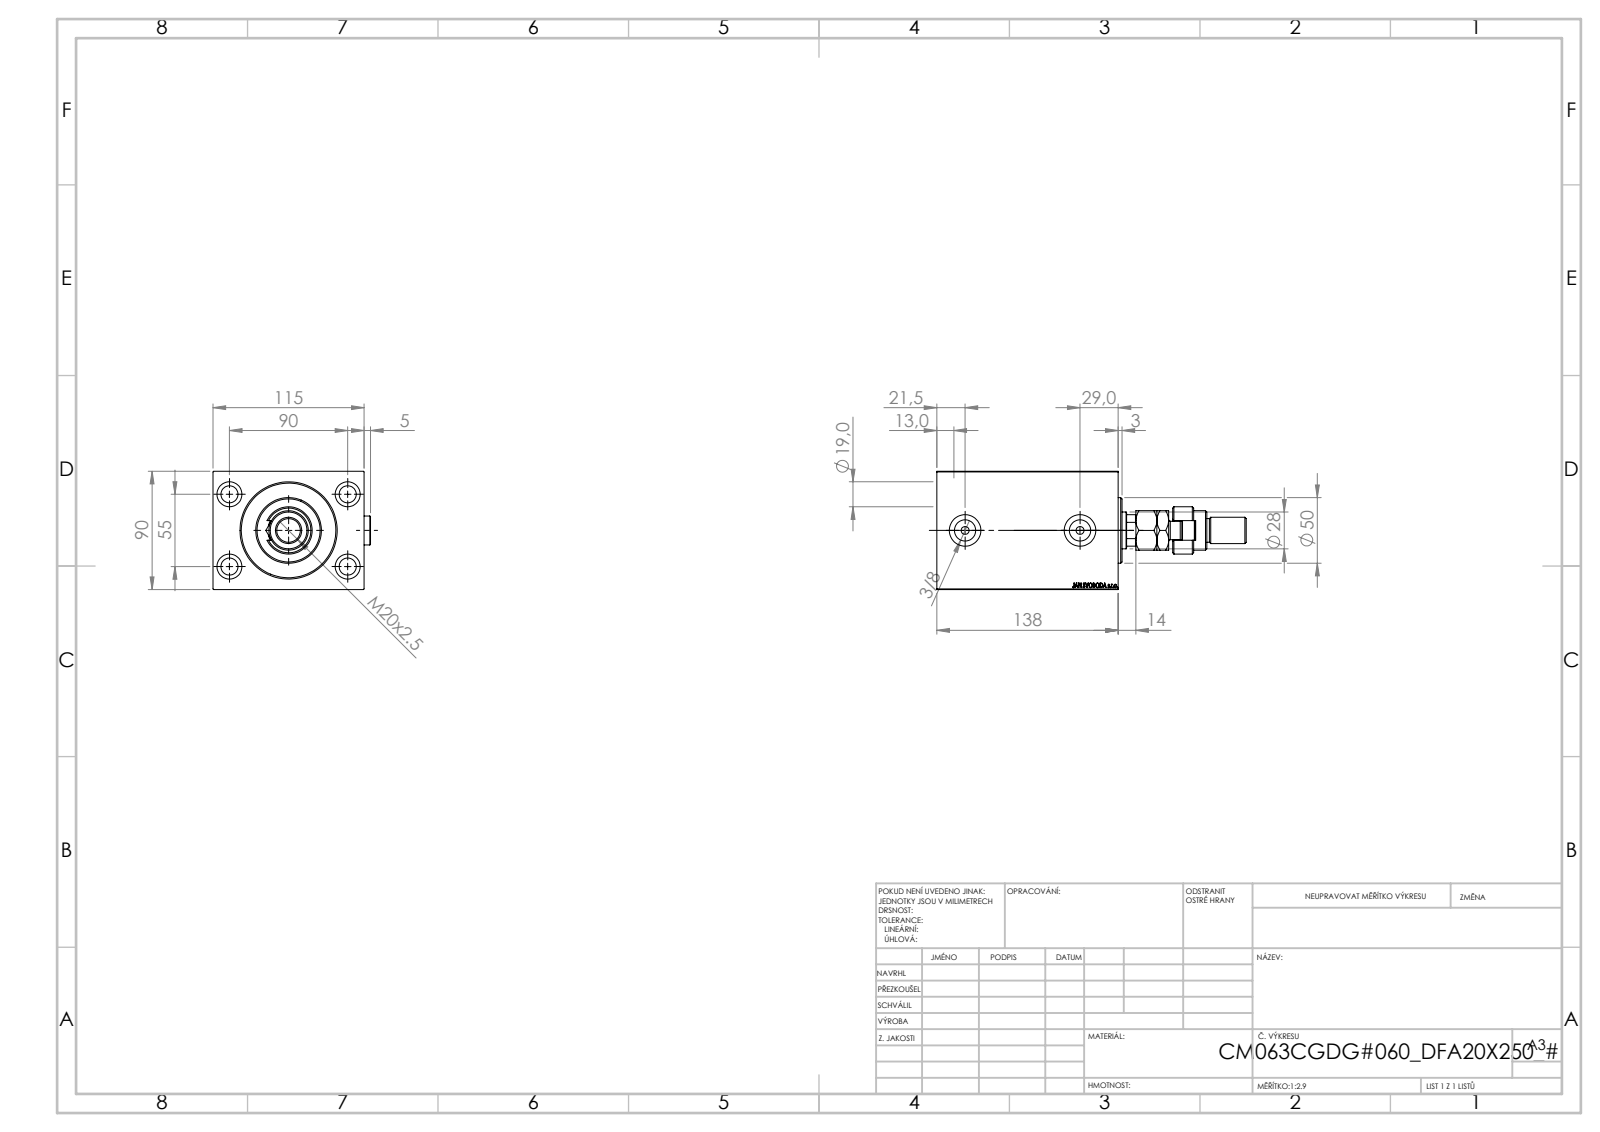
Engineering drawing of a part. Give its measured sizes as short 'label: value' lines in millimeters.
name: Zatka_OIL_PORT; MFA; V450CM_C_VCP; V450CM_VC_B (+2 more)
written by: SolidWorks 2019 (CONFIG_CONTROL_DESIGN)
unit: mm
bodies: 7 solids, 1004 faces (471 planar, 91 cylindrical, 442 other)
size: 235.5 × 119.9 × 90
volume: 1 233 000 mm³; area: 179 836 mm²
holes: 4× ⌀13, 4× ⌀19, 2× ⌀6, 2× ⌀16.17, 2× ⌀24, 1× ⌀18.5, 1× ⌀28, 1× ⌀31.5, 1× ⌀63, 1× ⌀65, 1× ⌀72
bosses: 3× ⌀22, 1× ⌀50, 1× ⌀36, 1× ⌀30, 1× ⌀20, 1× ⌀18, 1× ⌀14
rounds: 1× R7.5, 1× R12, 1× R13.5
face distances: 90, 115, 138, 17.5, 120.5, 13.5, 60, 107, 124.5, 64.5
hole spacings: 52.74, 55, 90, 105.48, 87.5
